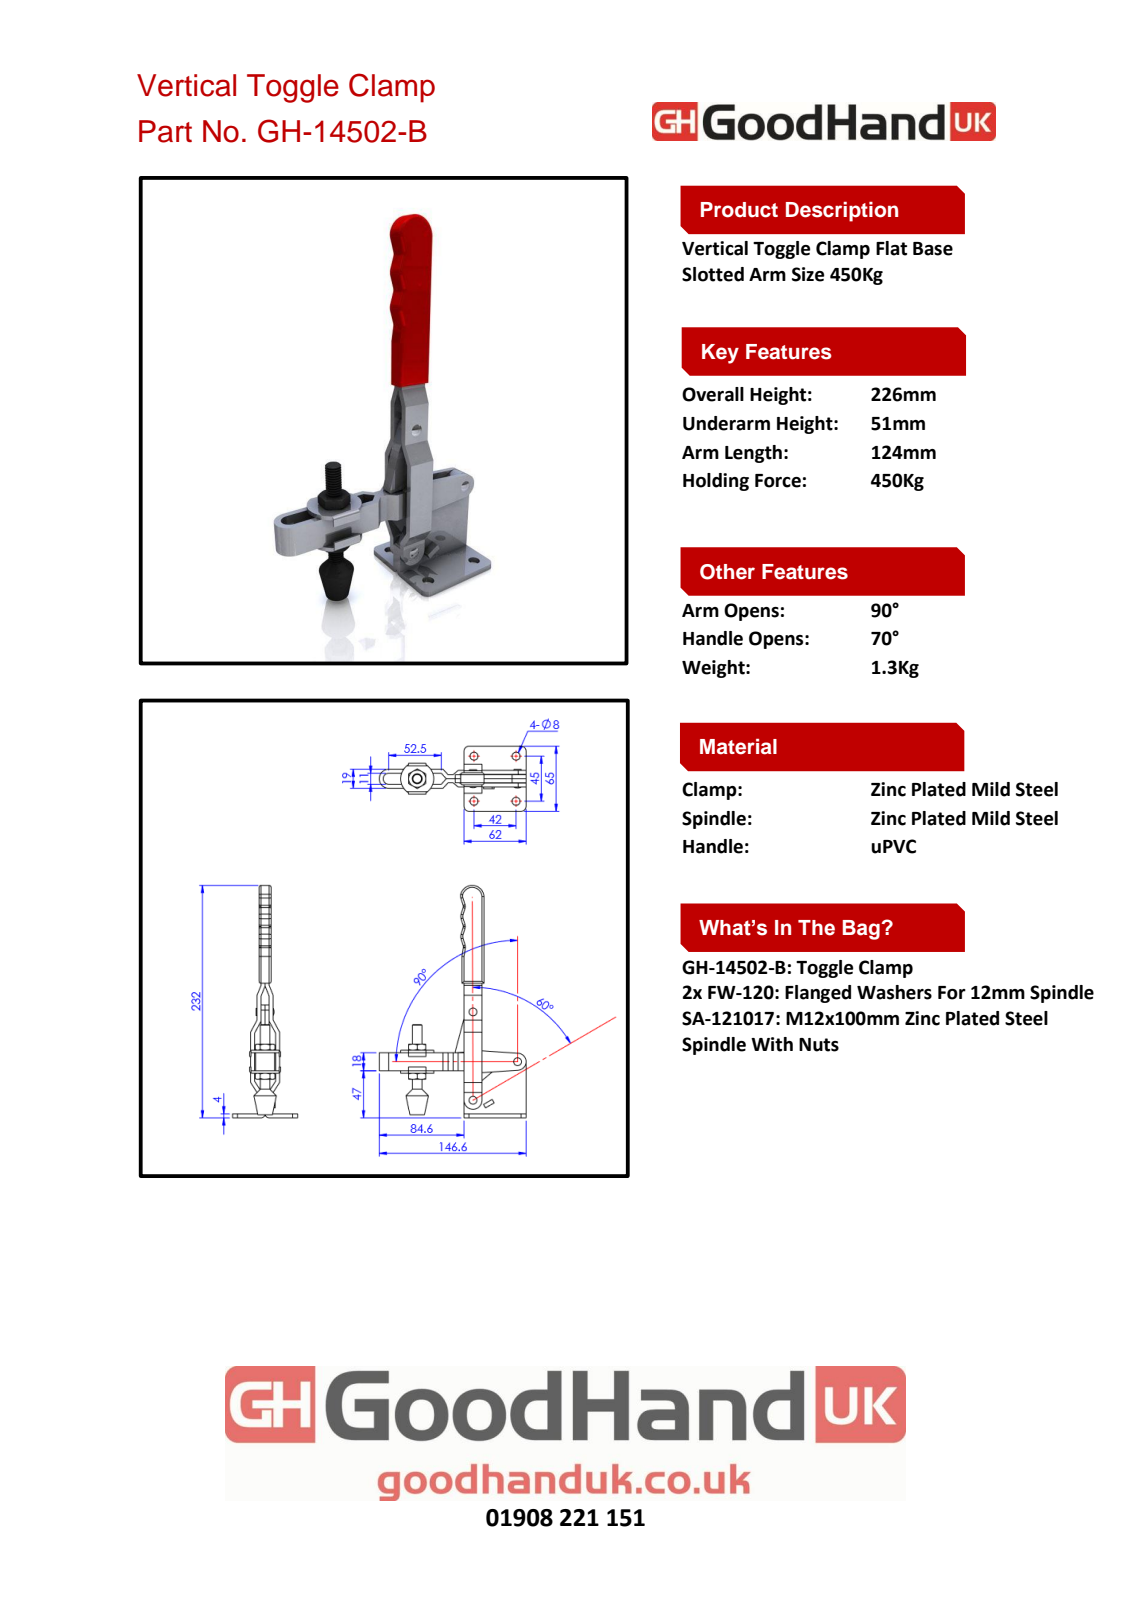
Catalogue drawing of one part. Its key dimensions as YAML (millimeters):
part_name: "4114541; 4114535; GH-14502-B 手把組合; 8202996 (+8 more)"
step_written_by: "SolidWorks 2016 (AUTOMOTIVE_DESIGN)"
units: millimeters
bodies: {solids: 17, faces: 425, planar: 140, cylindrical: 169, other: 116}
overall_size: [227.5, 177, 64]
volume: 166760
surface_area: 95898
round_holes:
  - {diameter: 8.7, count: 4}
  - {diameter: 9.03, count: 4}
  - {diameter: 12, count: 4}
  - {diameter: 6.2, count: 2}
  - {diameter: 9, count: 2}
  - {diameter: 4.2, count: 1}
round_bosses_or_shafts:
  - {diameter: 15, count: 2}
  - {diameter: 12.07, count: 2}
  - {diameter: 11.9, count: 2}
  - {diameter: 8.98, count: 2}
  - {diameter: 8.95, count: 2}
partial_cylinders:
  - {radius: 5.01, count: 10}
  - {radius: 8, count: 6}
  - {radius: 5, count: 3}
  - {radius: 10, count: 3}
  - {radius: 3, count: 2}
  - {radius: 3, count: 2}
  - {radius: 6, count: 2}
  - {radius: 9.75, count: 2}
face_to_face_distances: [5, 10, 1.35, 6.35, 11.35, 16.35, 15, 8, 6.65, 13]
hole_center_spacings: [32, 45, 55.22, 14.76, 21.2, 22.6, 30.04, 30.11]
